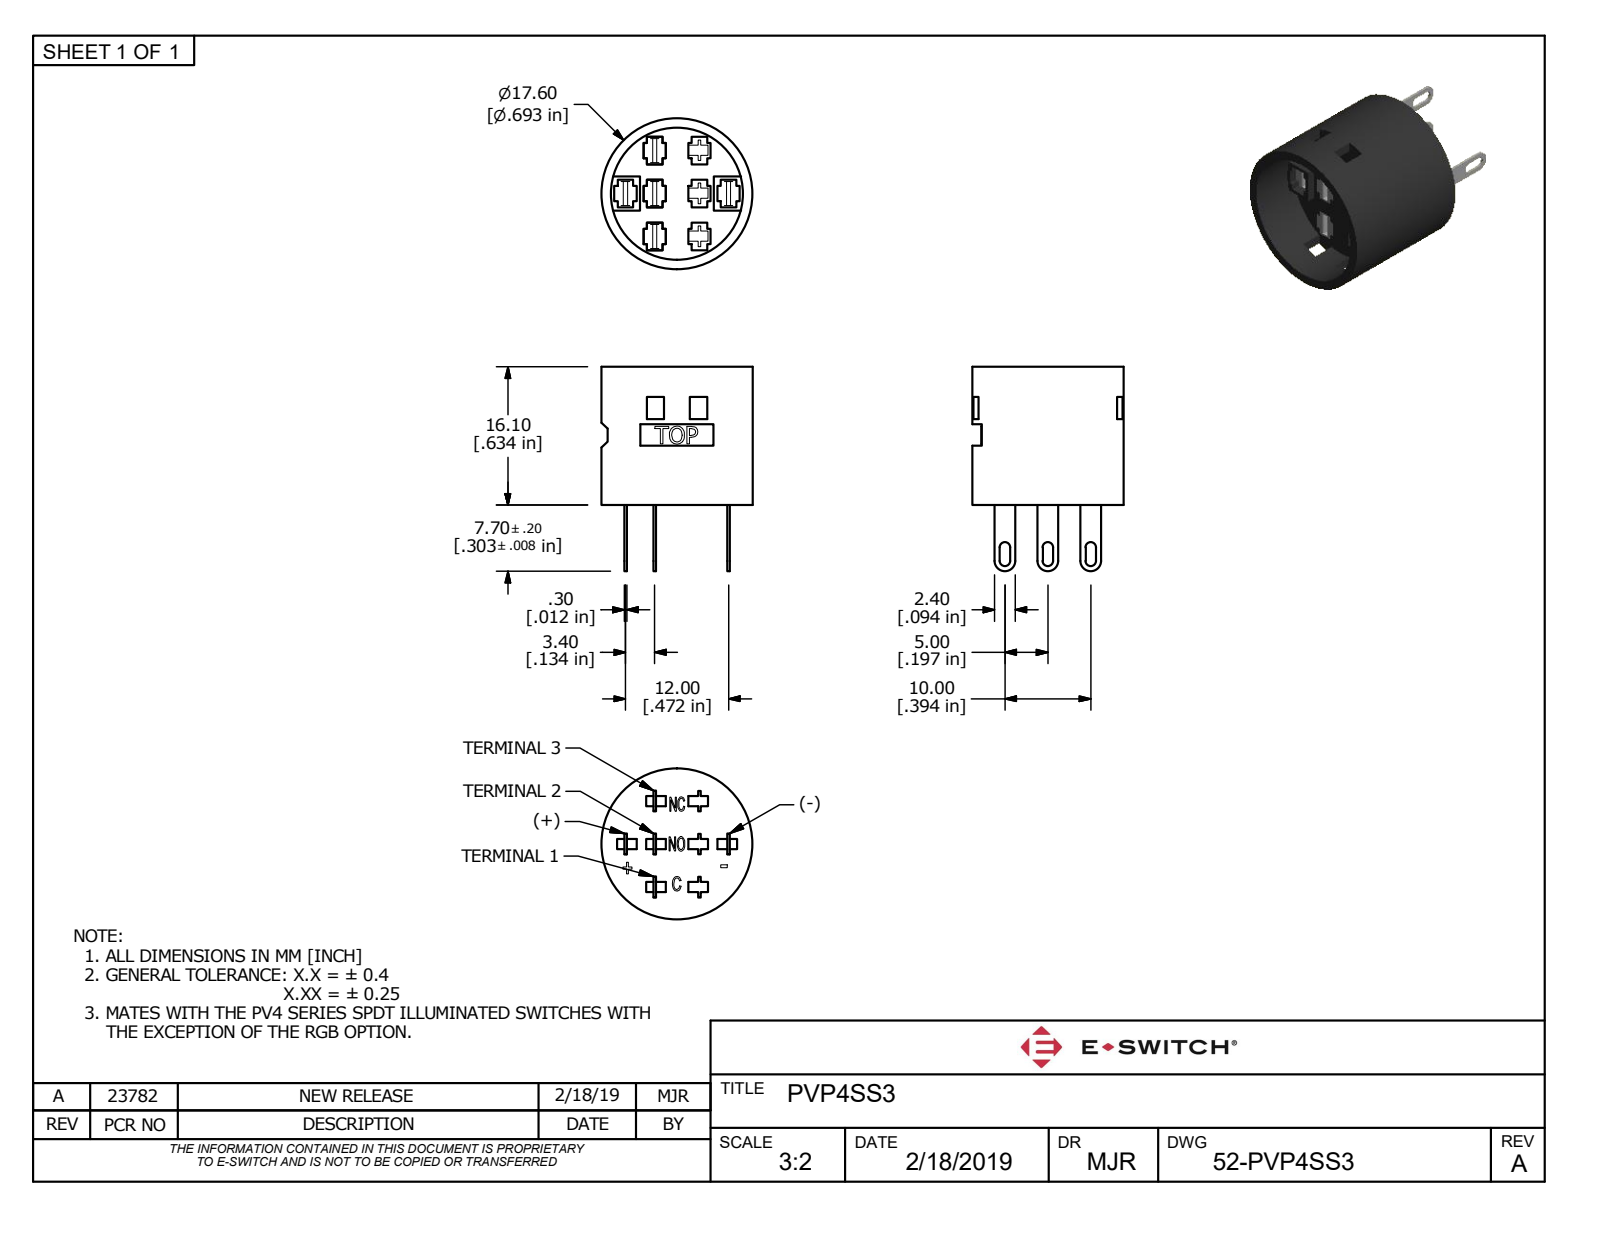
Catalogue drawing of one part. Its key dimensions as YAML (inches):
part_name: "PVP4SS3"
step_written_by: "Autodesk Inventor 2018 (AP242_MANAGED_MODEL_BASED_3D_ENGINEERING_MIM_LF)"
units: inches
bodies: {solids: 1, faces: 481, planar: 405, cylindrical: 27, other: 49}
overall_size: [0.941, 0.693, 0.693]
volume: 0.149
surface_area: 4.132
round_holes:
  - {diameter: 0.606, count: 1}
round_bosses_or_shafts:
  - {diameter: 0.693, count: 1}
partial_cylinders:
  - {radius: 0.01, count: 6}
  - {radius: 0.024, count: 6}
  - {radius: 0.047, count: 3}
face_to_face_distances: [0.016, 0.02, 0.39, 0.098, 0.071, 0.339, 0.197, 0.159, 0.163, 0.087]
